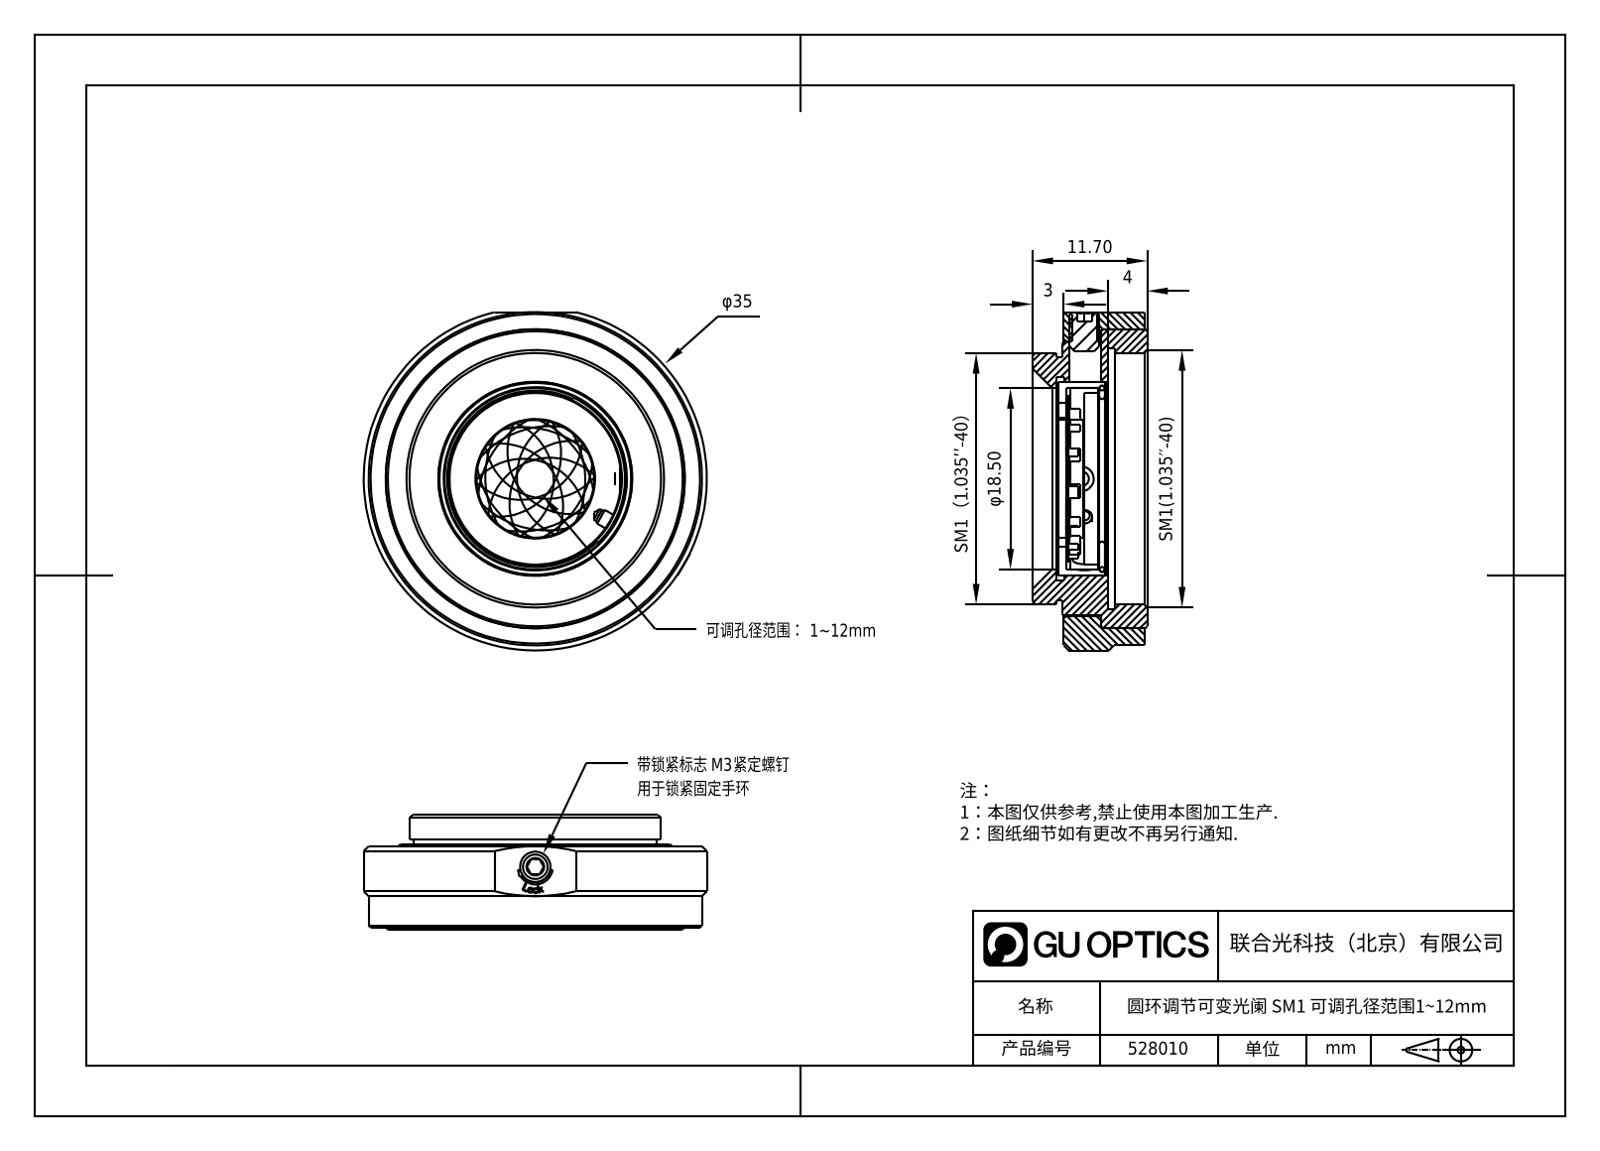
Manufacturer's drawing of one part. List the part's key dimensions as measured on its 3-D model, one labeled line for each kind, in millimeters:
Part name (STEP PRODUCT): 1.5.2.6_ZXL-H1D12A_SM1螺纹圆环式可调光阑，最大孔径12mm，Rev.A
STEP written by: SolidWorks 2021 (AUTOMOTIVE_DESIGN)
Units: millimetres
Bodies: 0 solids, 1393 faces (90 planar, 307 cylindrical, 996 other)
Overall size (bounding box): 36.95 × 35 × 11.7
Round holes (diameter × count): ⌀1.25 ×1, ⌀2.8 ×1, ⌀12 ×1, ⌀17.5 ×1, ⌀18.5 ×1, ⌀19.8 ×1, ⌀25.66 ×1, ⌀26.66 ×1, ⌀28 ×1, ⌀30.5 ×1
Round bosses / shafts (diameter × count): ⌀1.5 ×20, ⌀35 ×1, ⌀34 ×1, ⌀24.86 ×1, ⌀19.75 ×1, ⌀2.4 ×1, ⌀1.6 ×1
Partial cylindrical surfaces — rounded edges, fillets, slot ends (radius × count): R6.38 ×10, R1.75 ×1, R2.05 ×1
Main face-to-face distances: 8.5, 4.5, 4.2, 0.45, 4.05, 0.5, 4, 0.7, 1, 1.15
